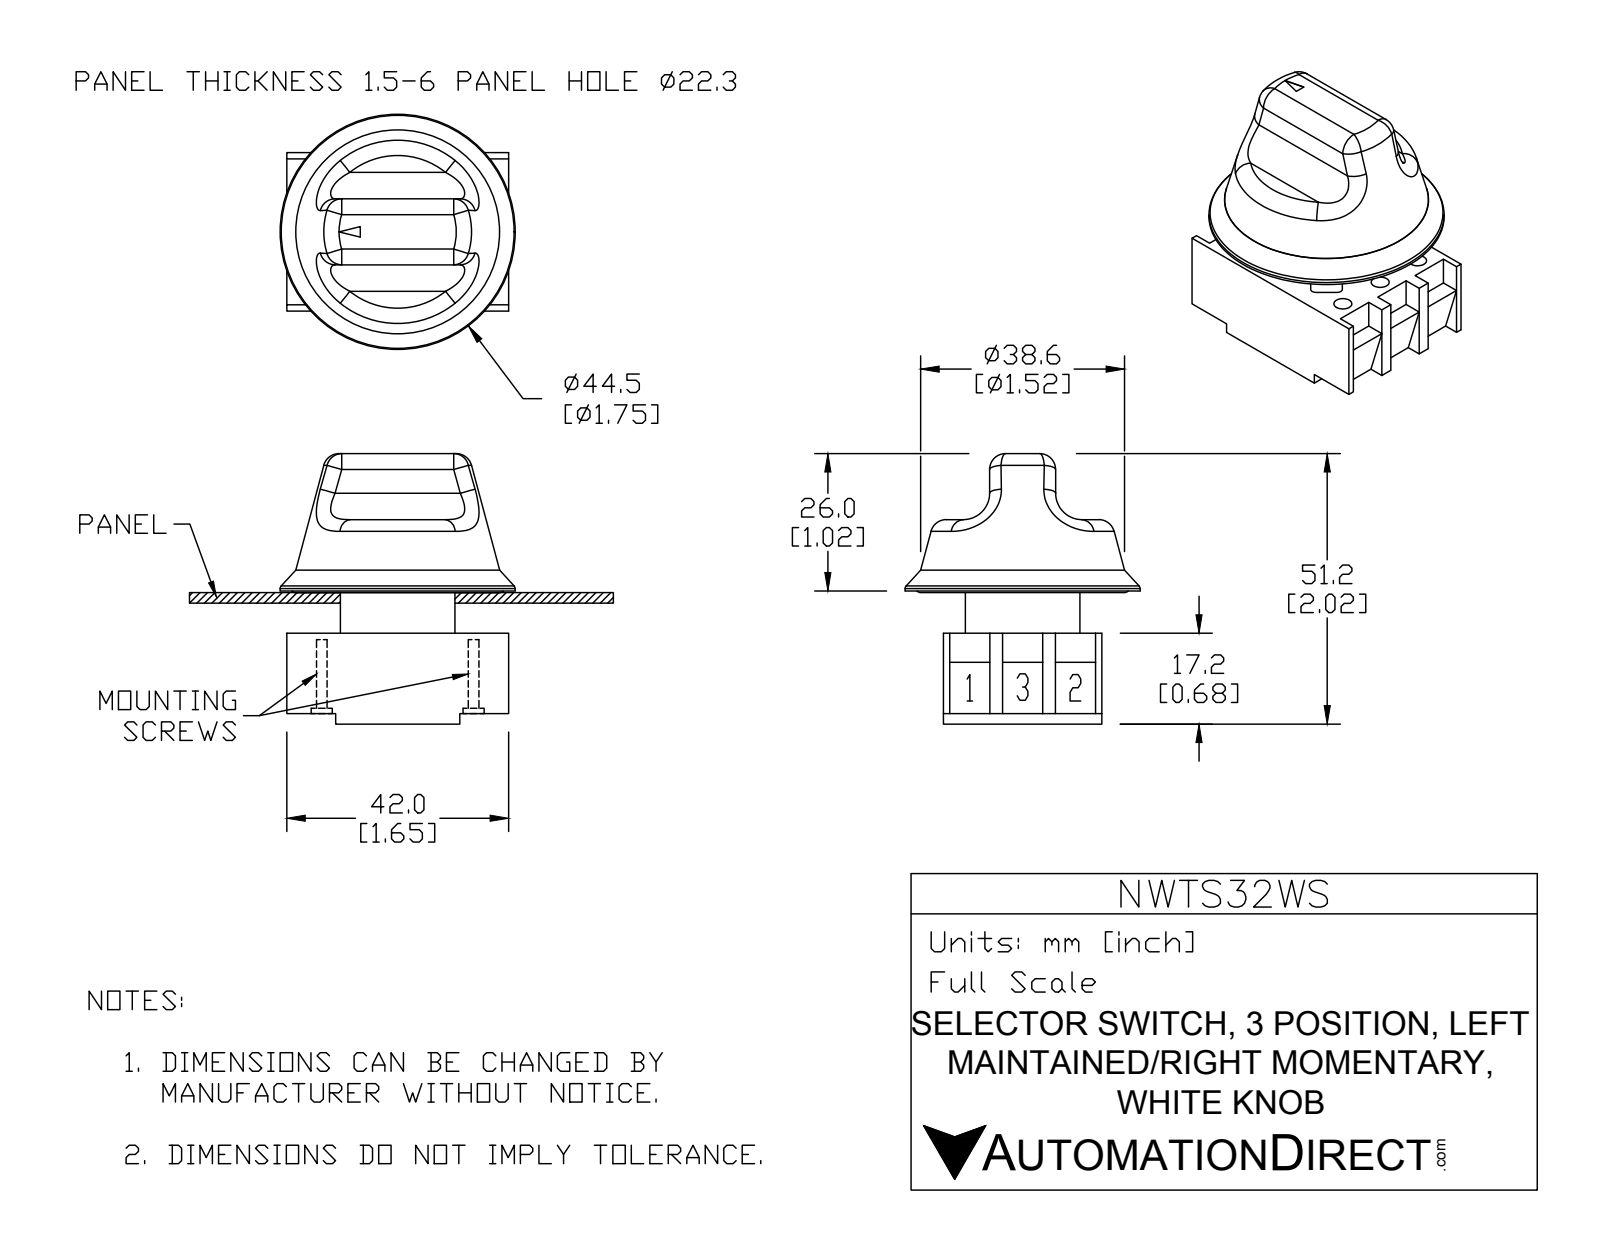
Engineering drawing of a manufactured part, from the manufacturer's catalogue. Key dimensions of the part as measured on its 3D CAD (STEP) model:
Part name (STEP PRODUCT): NWTS32WS
STEP written by: SolidWorks 2015 (AUTOMOTIVE_DESIGN)
Units: millimetres
Bodies: 7 solids, 236 faces (134 planar, 67 cylindrical, 35 other)
Overall size (bounding box): 51.2 × 44.5 × 44.5
Volume: 35 027 mm³ · Surface area: 19 099 mm²
Round holes (diameter × count): ⌀3.4 ×6, ⌀5 ×6, ⌀12.5 ×1
Round bosses / shafts (diameter × count): ⌀4.6 ×2, ⌀4 ×2, ⌀44.5 ×1, ⌀21.7 ×1
Partial cylindrical surfaces — rounded edges, fillets, slot ends (radius × count): R1 ×8, R8.7 ×5, R3 ×2, R5 ×2, R11 ×1
Main face-to-face distances: 3.95, 30, 8, 11.95, 7.7, 4.25, 10, 15.2, 22.9, 23.2
Hole centre spacings: 10, 17.52, 30.45, 28.76, 14.38, 20, 35.03
